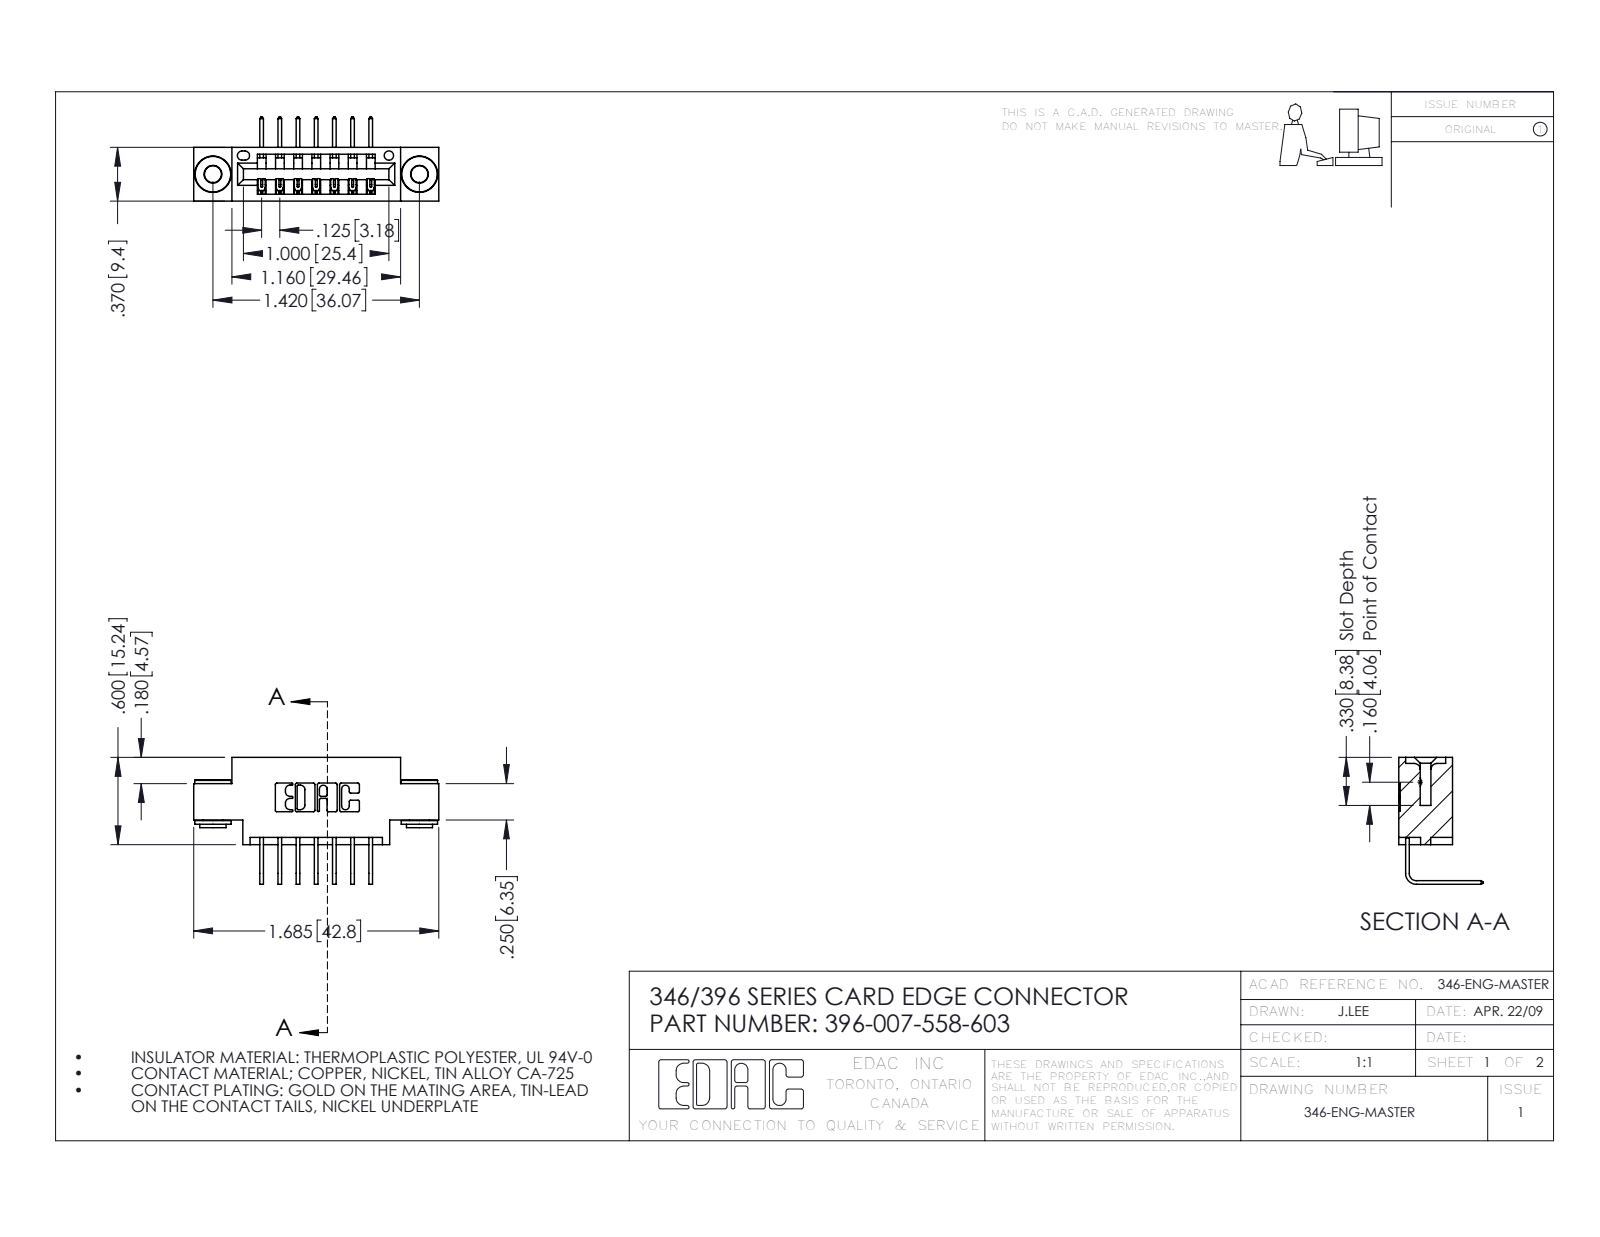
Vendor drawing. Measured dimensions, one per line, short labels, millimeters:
name: 396-007-558-603; 345-292-001_558 Tail - 2; 345-250-002_345-250-002-102; 346 Part_0.170 Offset - 0.156 Dia-TH
written by: SolidWorks 2016 (CONFIG_CONTROL_DESIGN)
unit: mm
bodies: 10 solids, 584 faces (384 planar, 192 cylindrical, 8 other)
size: 42.8 × 22.2 × 14.7
volume: 3 740 mm³; area: 4 820 mm²
holes: 2× ⌀2.9, 2× ⌀4, 1× ⌀1.6
bosses: 2× ⌀6.4, 2× ⌀4.6, 2× ⌀3.5
rounds: 22× R0.3, 14× R0.2, 6× R0.2, 6× R0.8, 3× R0.7, 2× R0.8, 2× R1, 1× R0.4
face distances: 6.4, 9.4, 8.2, 1.2, 0.6, 7.6, 3.8, 5.6, 2.5, 4.4
hole spacings: 6.2, 30.9, 36.1
